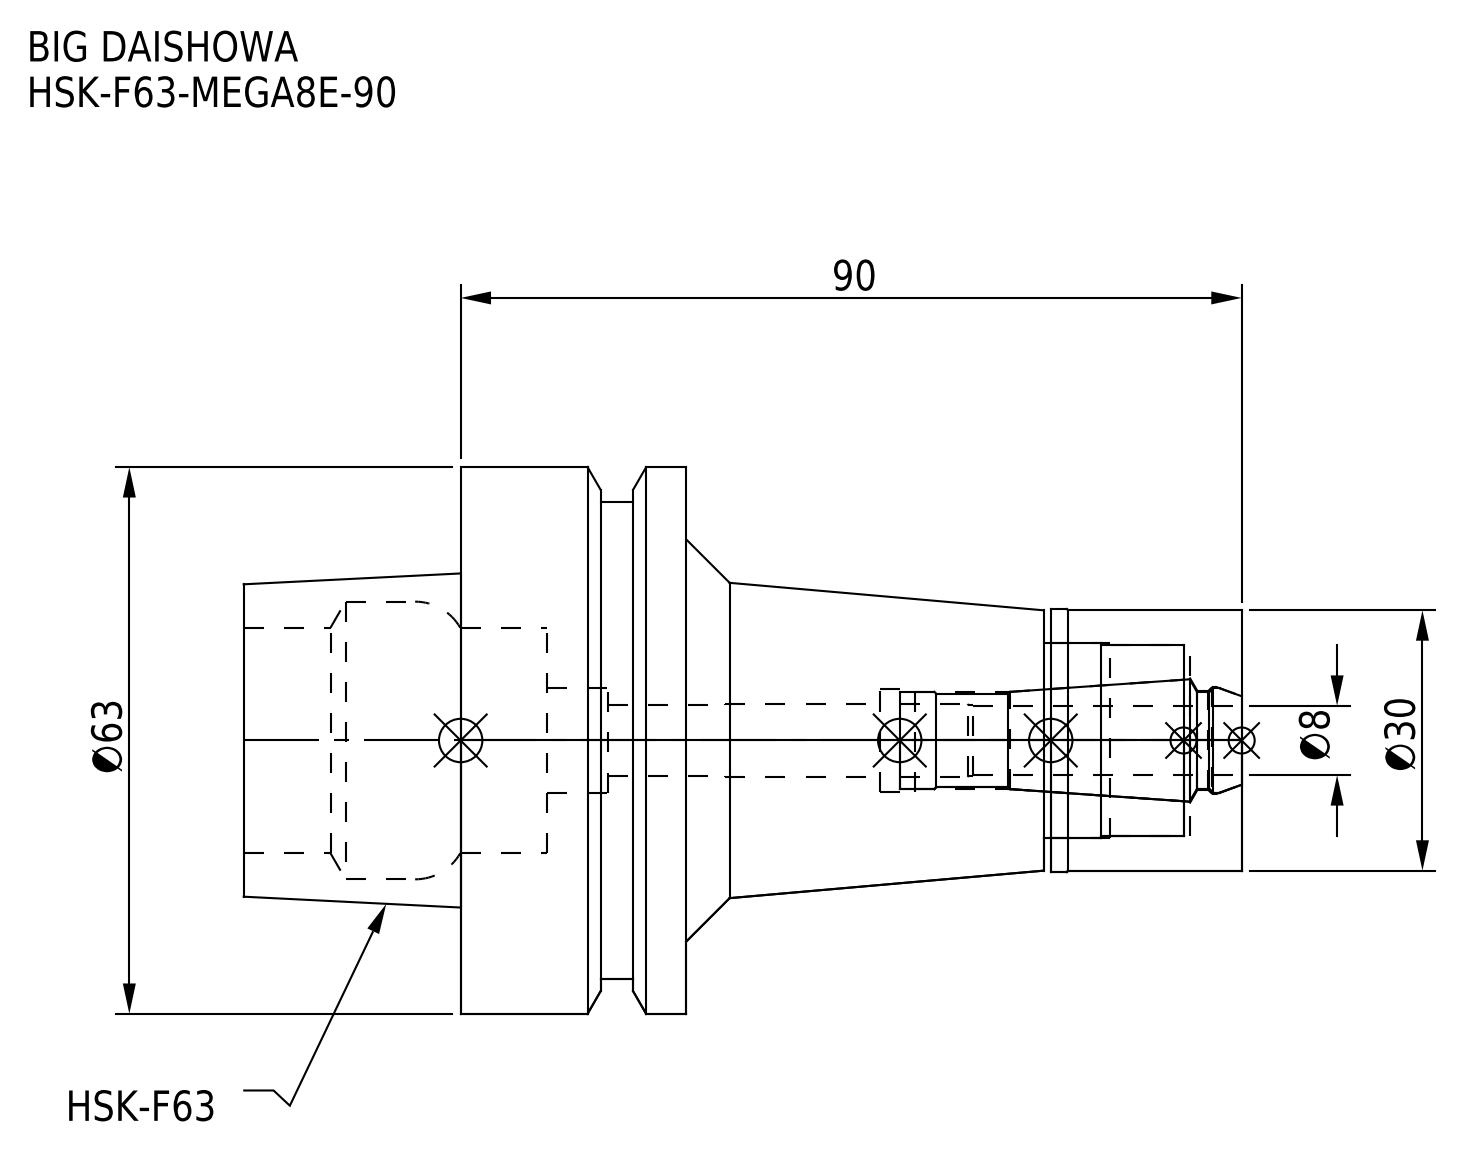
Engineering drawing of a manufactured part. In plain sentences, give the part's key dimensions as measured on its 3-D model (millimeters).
The part is named "HSK-F63-MEGA8E-90_1.stp; HF63ME08090-080_ASM.stp; HSK-F63-MEGA8E-90; HSK-F63-MEGA8E-90-080.stp (+3 more)". Its 3-D file was written by "SolidWorks 2019 (CONFIG_CONTROL_DESIGN)". It is 2 solids with 81 faces: 17 planar, 40 cylindrical and 24 other. Overall it measures 115 by 63 by 63 millimeters. Its volume is 129 358 cubic millimeters and its surface area 30 226 square millimeters. Round holes: 1 of diameter 8.25, 1 of diameter 8.4, 1 of diameter 11.2, 1 of diameter 11.4, 1 of diameter 11.8, 1 of diameter 12, 1 of diameter 12.3, 1 of diameter 22, 1 of diameter 22.5, 1 of diameter 26, 1 of diameter 32. Round bosses or shafts: 1 of diameter 63, 1 of diameter 55, 1 of diameter 30.3, 1 of diameter 30. The main face-to-face distances are 26, 64, 90, 115, 51, 25, 80.05, 16.05, 9.95, 34.95.
